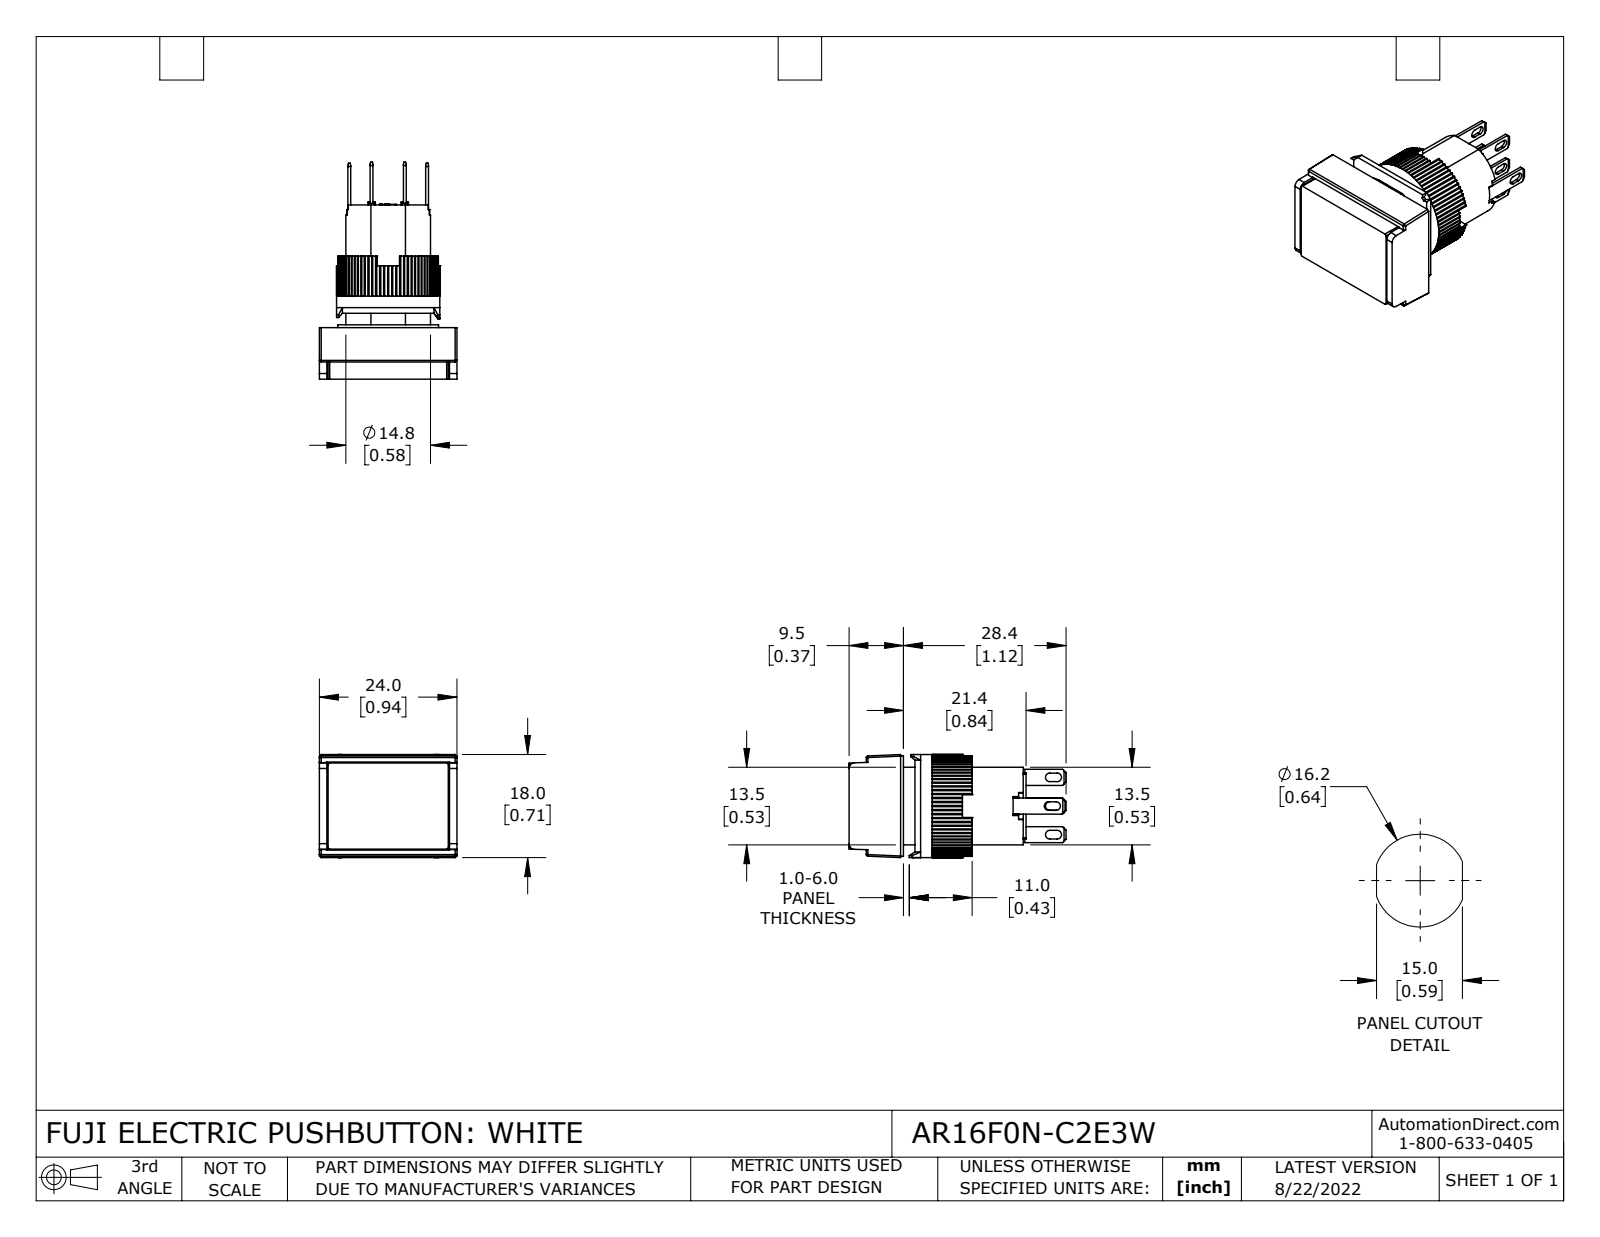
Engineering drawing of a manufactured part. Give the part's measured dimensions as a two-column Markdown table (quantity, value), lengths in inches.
| quantity | value |
| --- | --- |
| part name | AR16F0N-C2E3W |
| STEP written by | SolidWorks 2021 (CONFIG_CONTROL_DESIGN) |
| units | inches |
| bodies | 14 solids, 843 faces (656 planar, 183 cylindrical, 4 other) |
| overall size | 1.492 × 0.945 × 0.709 |
| volume | 0.444 in³ |
| surface area | 9.306 in² |
| round holes (diameter × count) | 0.543 × 1, 0.583 × 1 |
| round bosses / shafts (diameter × count) | 0.709 × 1, 0.693 × 1 |
| partial cylindrical surfaces (radius × count) | 0.01 × 80, 0.008 × 12, 0.03 × 8, 0.012 × 6, 0.039 × 2 |
| main face-to-face distances | 0.213, 0.354, 0.142, 0.35, 0.492, 0.138, 0.02, 0.843, 0.059, 0.453 |
